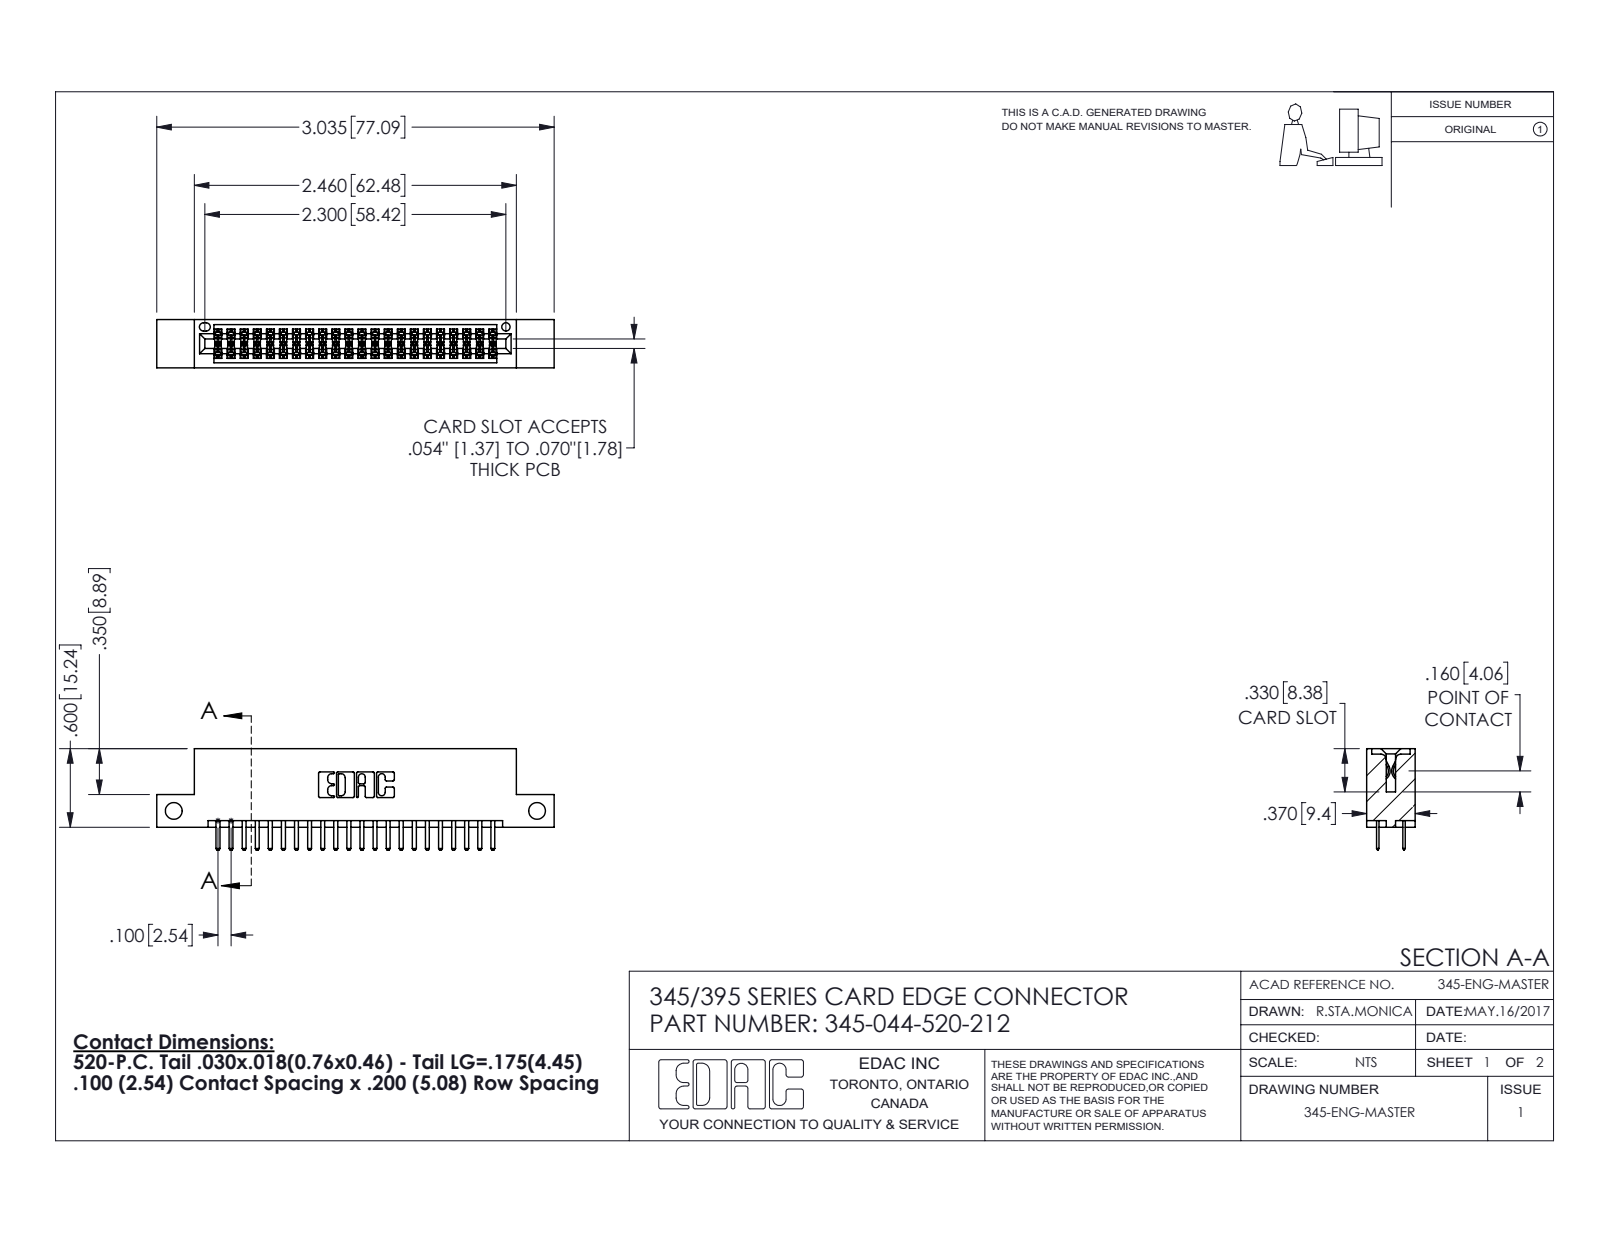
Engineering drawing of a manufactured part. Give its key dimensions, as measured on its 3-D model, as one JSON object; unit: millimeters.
{"part_name": "345 Part_Flush Mounting Lugs - Side Mount; 345-044-520-212; 345-292-001_345-293-120", "step_written_by": "SolidWorks 2016 (CONFIG_CONTROL_DESIGN)", "units": "millimeters", "bodies": {"solids": 45, "faces": 2502, "planar": 1620, "cylindrical": 882, "other": 0}, "overall_size": [77.1, 19.7, 9.4], "volume_mm3": 7190, "surface_area_mm2": 10070, "round_holes": [[3.3, 2], [1.6, 1]], "partial_cylinders_radius": [[0.2, 66], [0.3, 48], [0.3, 22], [0.2, 6], [0.8, 6], [0.7, 3], [0.4, 2], [0.5, 2]], "face_to_face_distances": [5.1, 7.6, 1.8, 9.4, 2.5, 6.9, 0.6, 5.7, 0.6, 1.8], "hole_center_spacings": [70.5]}
